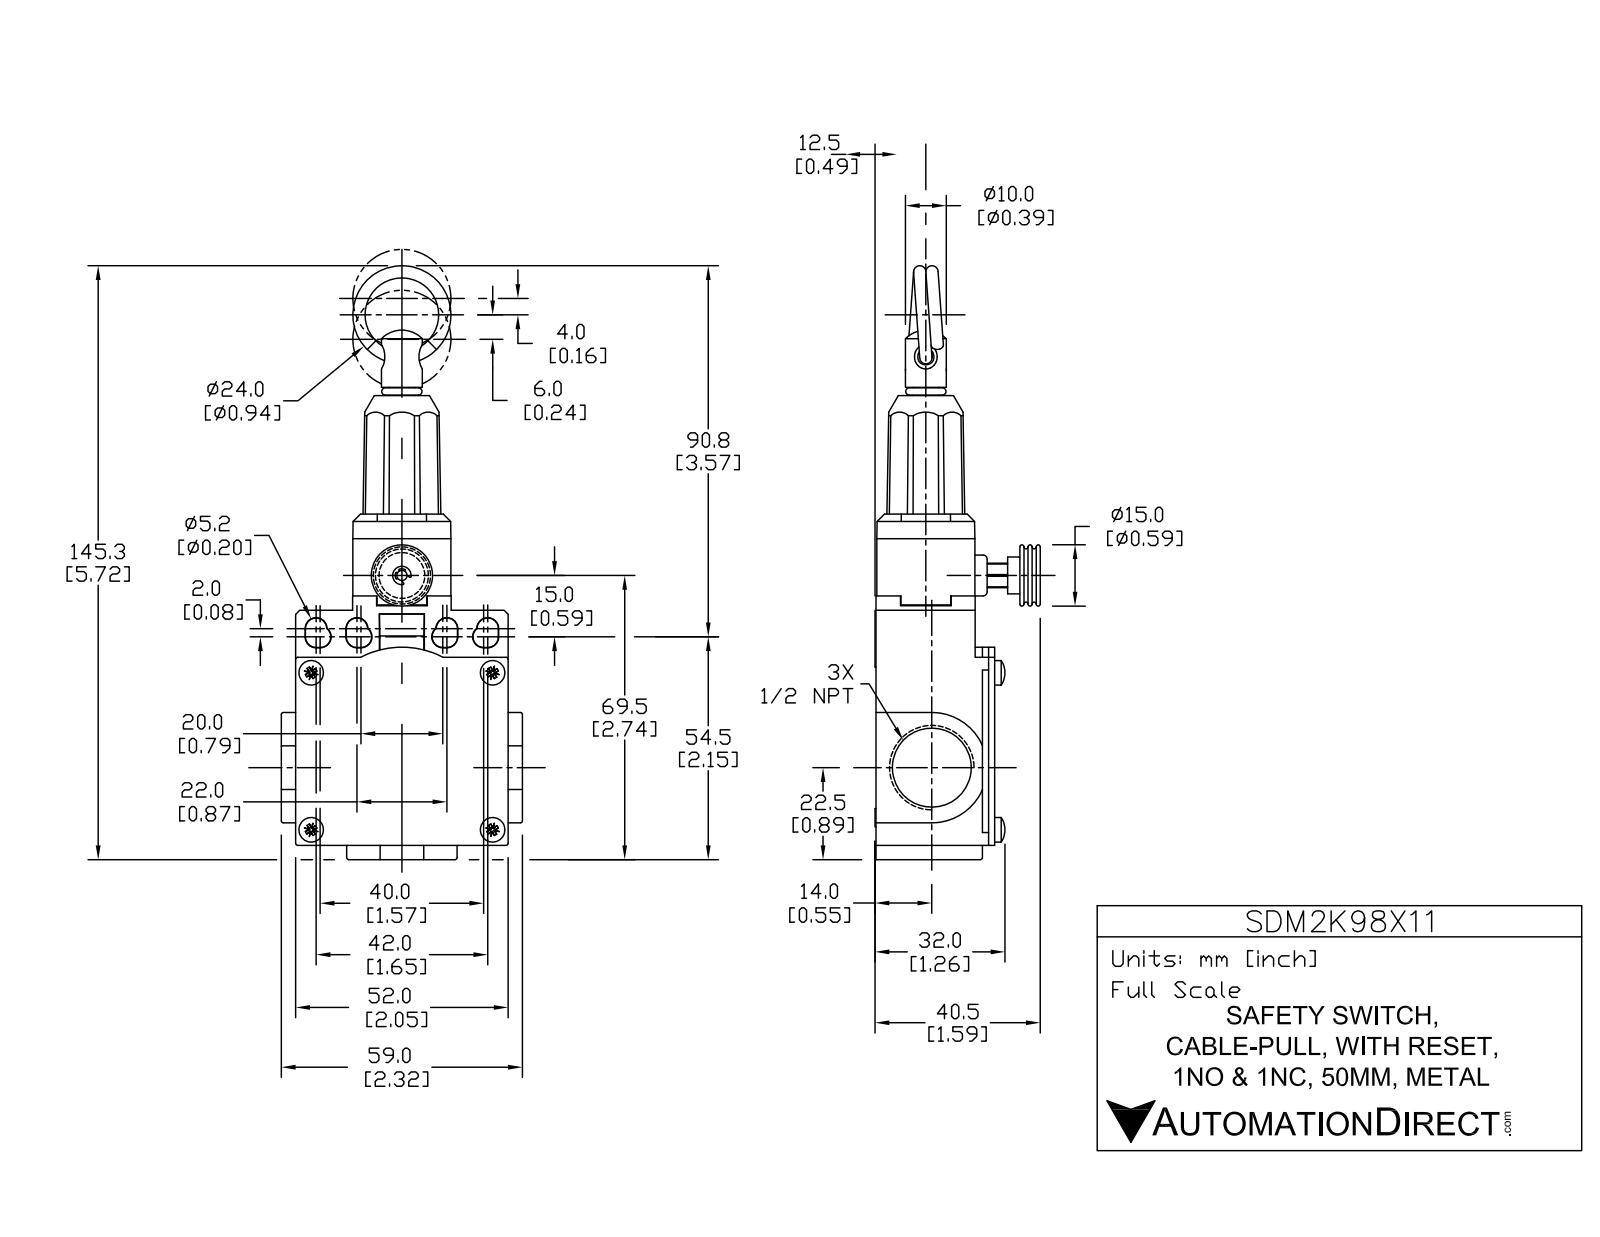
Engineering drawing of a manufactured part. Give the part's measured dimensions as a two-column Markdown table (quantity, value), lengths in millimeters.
| quantity | value |
| --- | --- |
| part name | SDM2K98X11 |
| STEP written by | SolidWorks 2017 (AUTOMOTIVE_DESIGN) |
| units | millimeters |
| bodies | 5 solids, 281 faces (119 planar, 105 cylindrical, 57 other) |
| overall size | 146.5 × 59 × 38.3 |
| volume | 105 900 mm³ |
| surface area | 26 240 mm² |
| round holes (diameter × count) | 17 × 2, 19 × 2, 4 × 1, 10.1 × 1, 15 × 1 |
| round bosses / shafts (diameter × count) | 5.6 × 4, 5.5 × 4, 10 × 2, 9.8 × 1, 6.3 × 1, 2.5 × 1 |
| partial cylindrical surfaces (radius × count) | 2.6 × 12, 0.5 × 10, 3 × 4, 13.5 × 2, 3.4 × 1, 10 × 1, 10.2 × 1, 22 × 1 |
| main face-to-face distances | 29.1, 3.5, 14, 24, 2.5, 6, 38, 52, 5.1, 35.5 |
| hole center spacings | 1.8, 101.5 |
